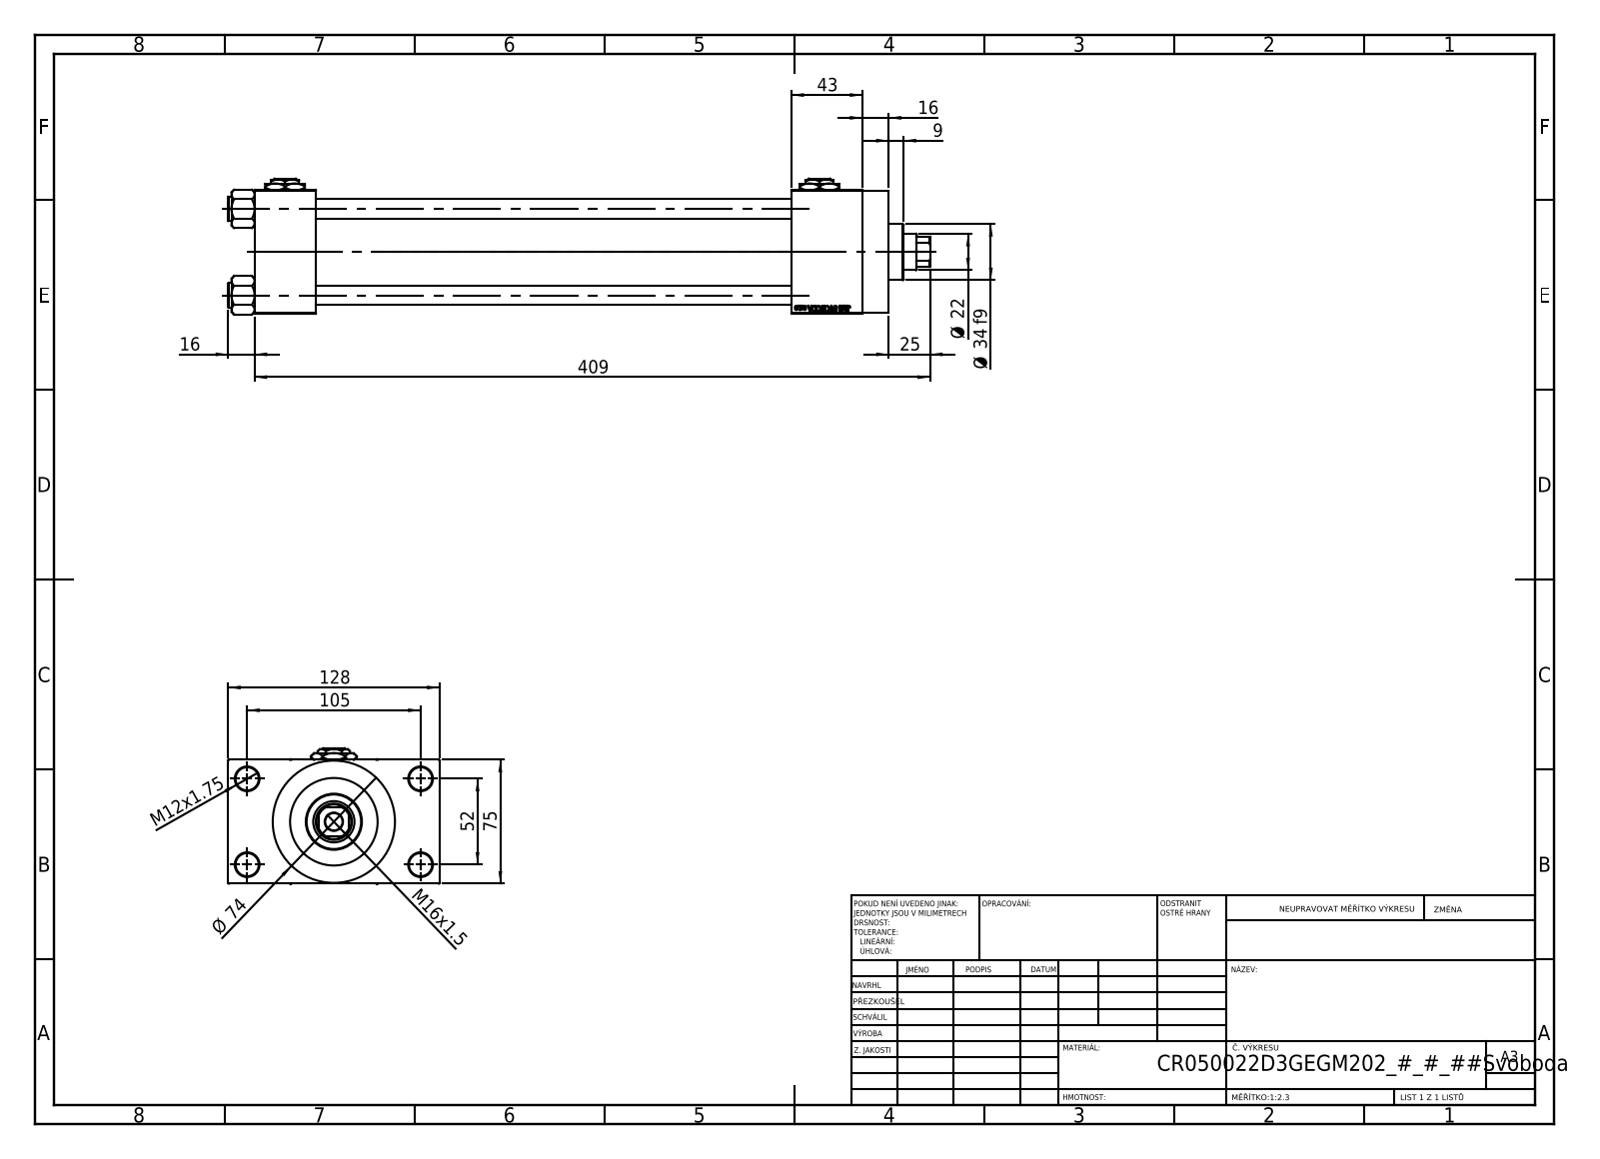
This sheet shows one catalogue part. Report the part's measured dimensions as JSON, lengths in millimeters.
{"part_name": "V215_VC_A; V215CR_VCP_D; Zatka_pro_OIL_PORT; NUT_M5_D (+2 more)", "step_written_by": "SolidWorks 2019 (CONFIG_CONTROL_DESIGN)", "units": "millimeters", "bodies": {"solids": 13, "faces": 1205, "planar": 545, "cylindrical": 100, "other": 560}, "overall_size": [425, 128, 82.27], "volume_mm3": 1109000, "surface_area_mm2": 296355, "round_holes": [[12, 4], [14, 4], [7, 2], [20.96, 2], [30, 2], [10.5, 1], [22, 1], [25, 1], [41, 1], [50, 1], [53, 1]], "round_bosses_or_shafts": [[15, 4], [74, 1], [56, 1], [34, 1]], "partial_cylinders_radius": [[10.5, 1]], "face_to_face_distances": [75, 288, 37, 325, 26.5, 101.5, 368, 331, 43, 16], "hole_center_spacings": [26.35, 36.98, 52.3, 58.43, 58.59, 78.65, 94.37, 52]}
